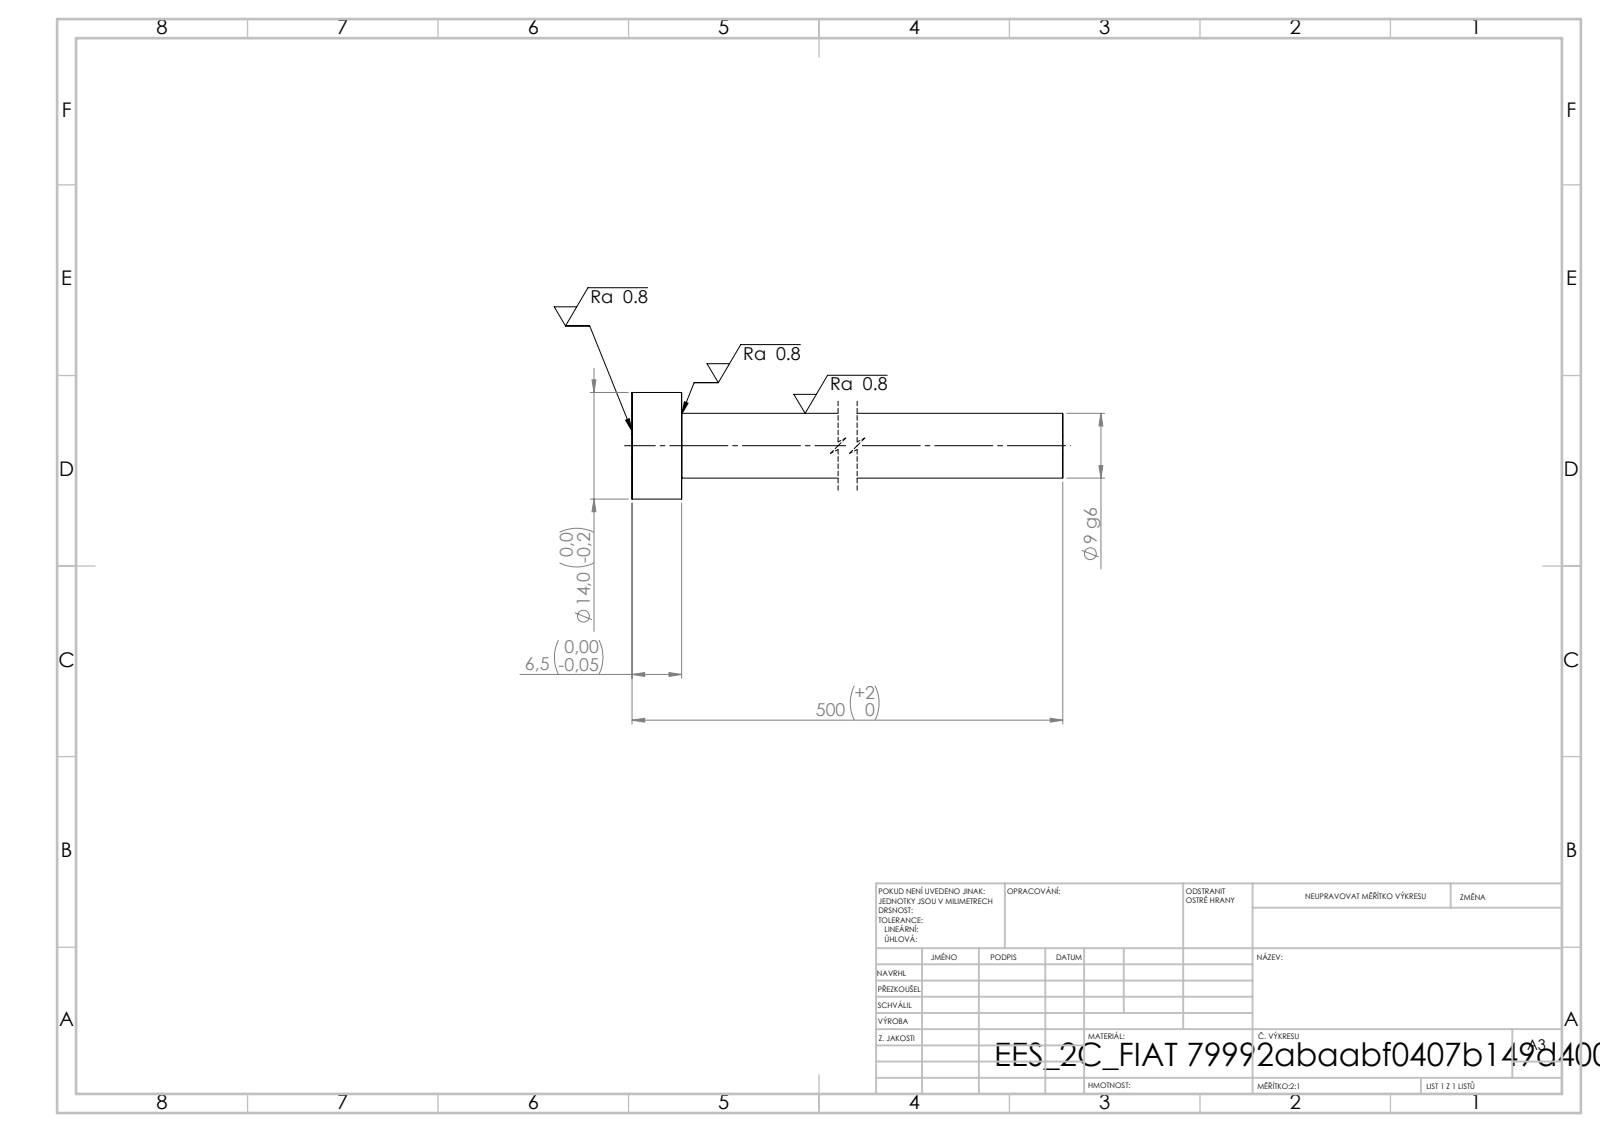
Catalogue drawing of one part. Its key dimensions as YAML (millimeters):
step_written_by: "SolidWorks 2019 (CONFIG_CONTROL_DESIGN)"
units: millimeters
bodies: {solids: 1, faces: 7, planar: 3, cylindrical: 4, other: 0}
overall_size: [500, 14, 14]
volume: 29004
surface_area: 13772
round_bosses_or_shafts:
  - {diameter: 14, count: 1}
  - {diameter: 8.5, count: 1}
face_to_face_distances: [6.5, 500, 493.5]
